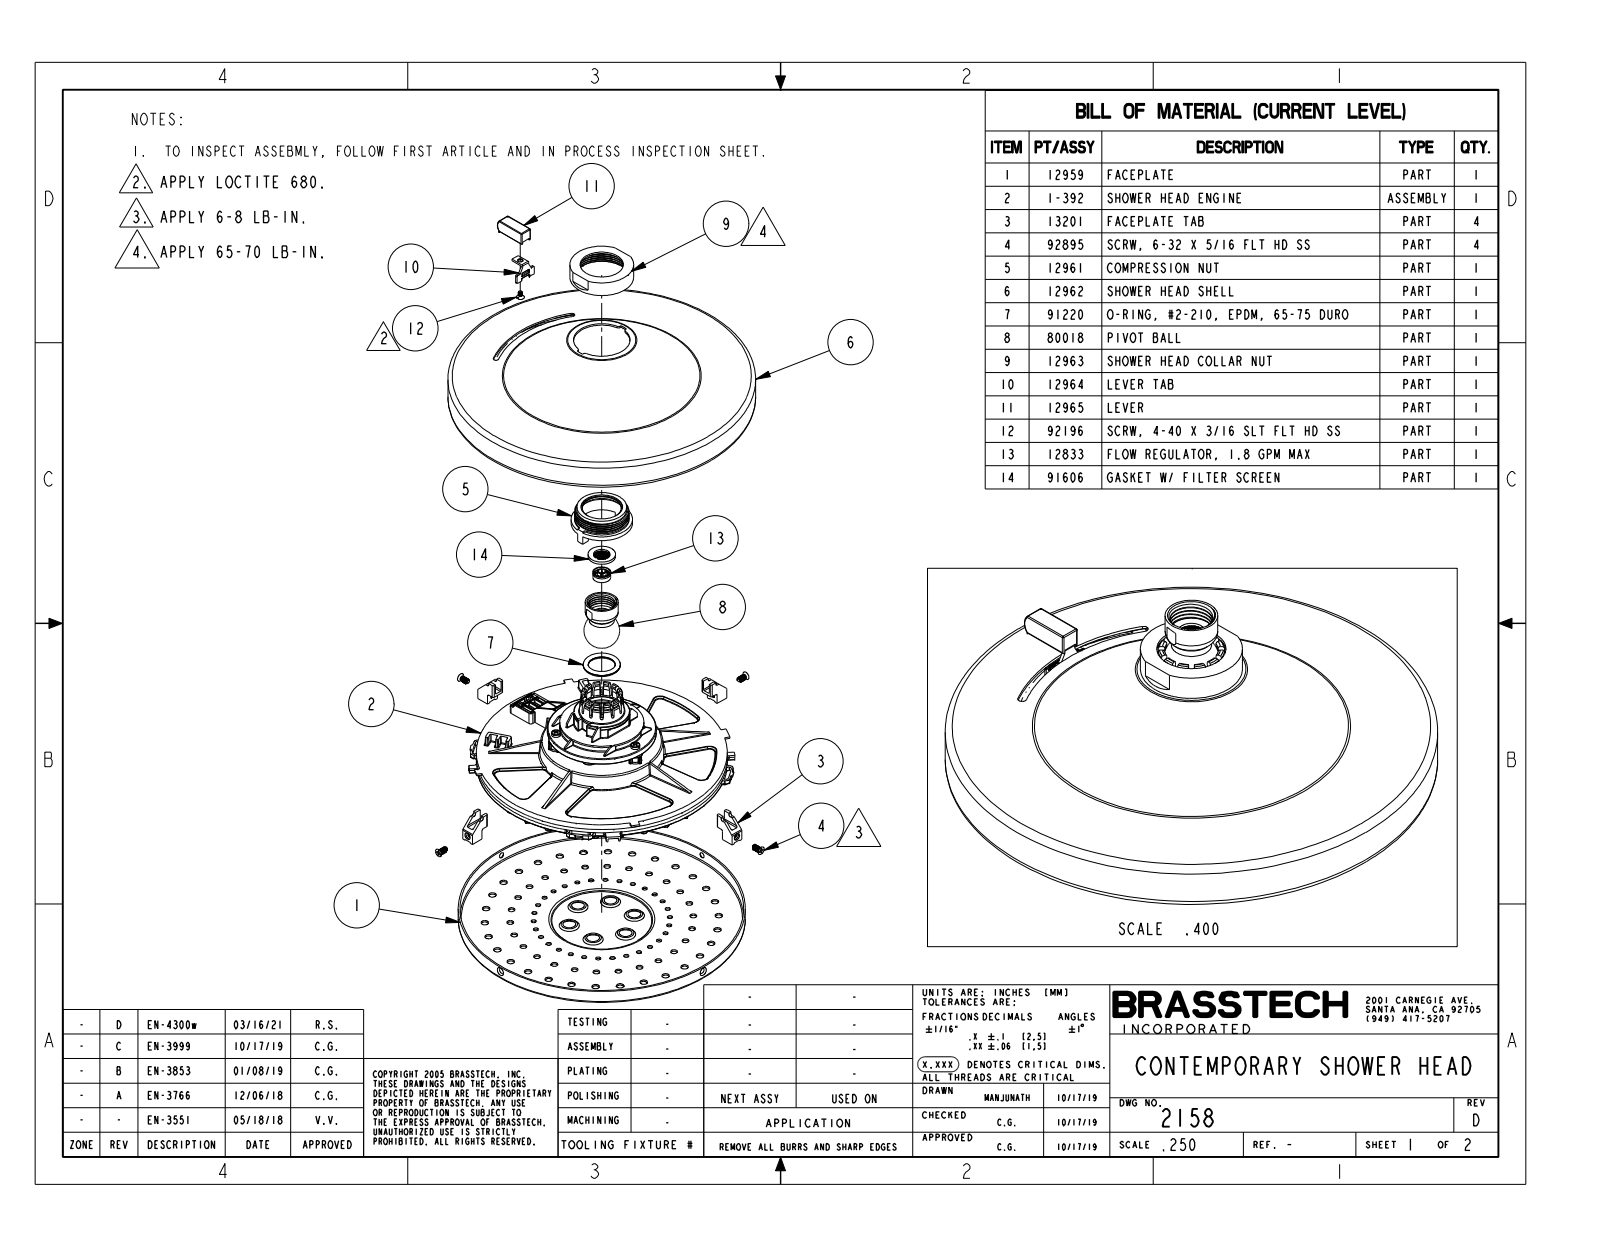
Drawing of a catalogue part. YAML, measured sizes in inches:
part_name: "12959; MANIFOLD_SOLID_BREP_129858; MANIFOLD_SOLID_BREP_191852; 4844-105_55_ASM (+8 more)"
step_written_by: "CREO PARAMETRIC BY PTC INC, 2018400 (AUTOMOTIVE_DESIGN)"
units: inches
bodies: {solids: 8, faces: 2451, planar: 486, cylindrical: 386, other: 1579}
overall_size: [8.45, 8.45, 3.274]
volume: 64.78
surface_area: 323
round_holes:
  - {diameter: 0.141, count: 30}
  - {diameter: 0.205, count: 30}
  - {diameter: 0.185, count: 26}
  - {diameter: 0.15, count: 1}
  - {diameter: 4.091, count: 1}
  - {diameter: 7.786, count: 1}
round_bosses_or_shafts:
  - {diameter: 0.236, count: 30}
  - {diameter: 0.22, count: 26}
  - {diameter: 8.45, count: 1}
  - {diameter: 7.88, count: 1}
  - {diameter: 3.37, count: 1}
  - {diameter: 2.213, count: 1}
  - {diameter: 1.75, count: 1}
  - {diameter: 0.905, count: 1}
partial_cylinders:
  - {radius: 0.039, count: 10}
  - {radius: 0.059, count: 10}
  - {radius: 0.169, count: 10}
  - {radius: 0.012, count: 9}
  - {radius: 0.02, count: 9}
  - {radius: 0.008, count: 4}
  - {radius: 0.02, count: 4}
  - {radius: 0.031, count: 4}
face_to_face_distances: [0.013, 0.047, 0.034, 0.823, 0.81, 0.776, 0.177, 0.164, 0.13, 0.646]
hole_center_spacings: [2.519, 4.46, 4.891, 2.861, 3.77, 4.709, 0.607, 1.206]
